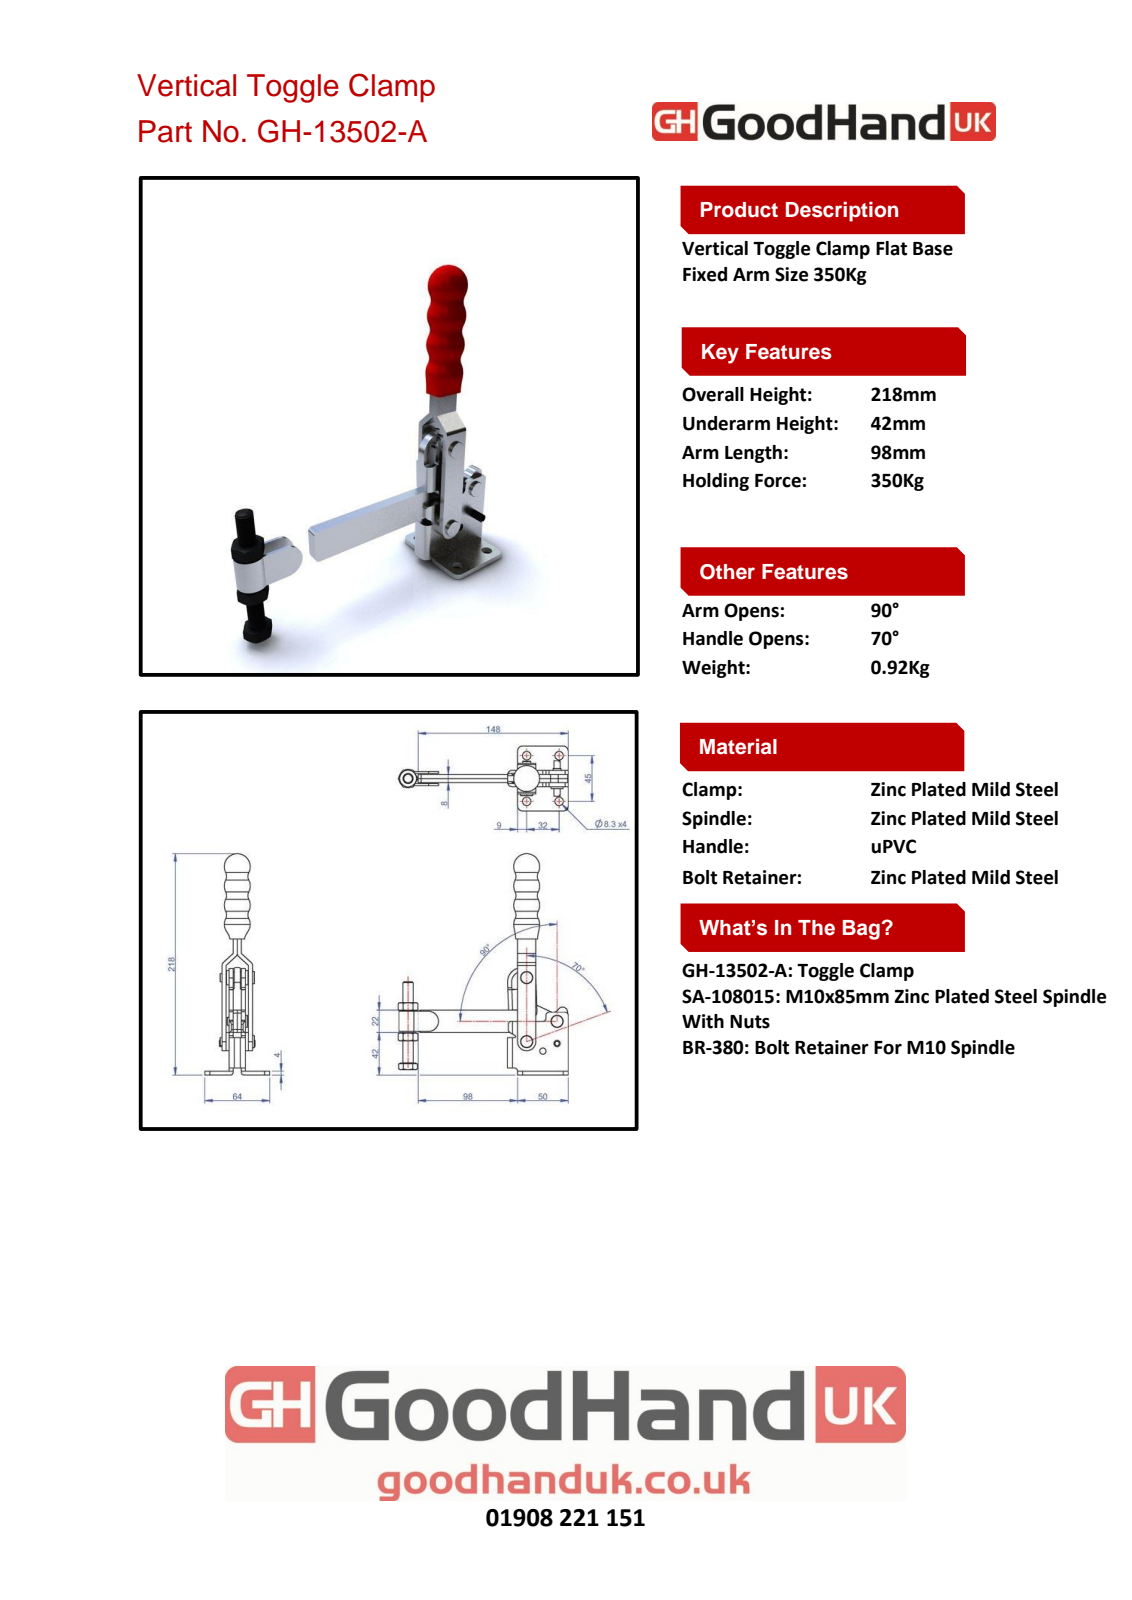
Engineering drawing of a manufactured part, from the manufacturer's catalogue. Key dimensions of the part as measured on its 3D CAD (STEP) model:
Part name (STEP PRODUCT): GH-13502-A(簡化)-1; Group1^GH-13502-A(簡化)-1; GH-SA-108015-1^GH-13502-A(簡化)-1; Group2^GH-13502-A(簡化)-1 (+3 more)
STEP written by: SolidWorks 2016 (AUTOMOTIVE_DESIGN)
Units: millimetres
Bodies: 5 solids, 324 faces (119 planar, 131 cylindrical, 74 other)
Overall size (bounding box): 220.4 × 191.97 × 64
Volume: 142 936 mm³ · Surface area: 66 947 mm²
Round holes (diameter × count): ⌀6 ×5, ⌀8.3 ×4, ⌀8.5 ×1, ⌀10 ×1
Round bosses / shafts (diameter × count): ⌀12 ×4, ⌀6 ×1
Partial cylindrical surfaces — rounded edges, fillets, slot ends (radius × count): R5 ×7, R1 ×6, R3 ×5, R9 ×5, R4.1 ×4, R2 ×2, R0.1 ×1, R6 ×1
Main face-to-face distances: 4, 8, 12, 11, 7, 15, 19, 16, 3, 22
Hole centre spacings: 32, 45, 55.22, 143.51, 175.19, 18.52, 30.04, 30.54
